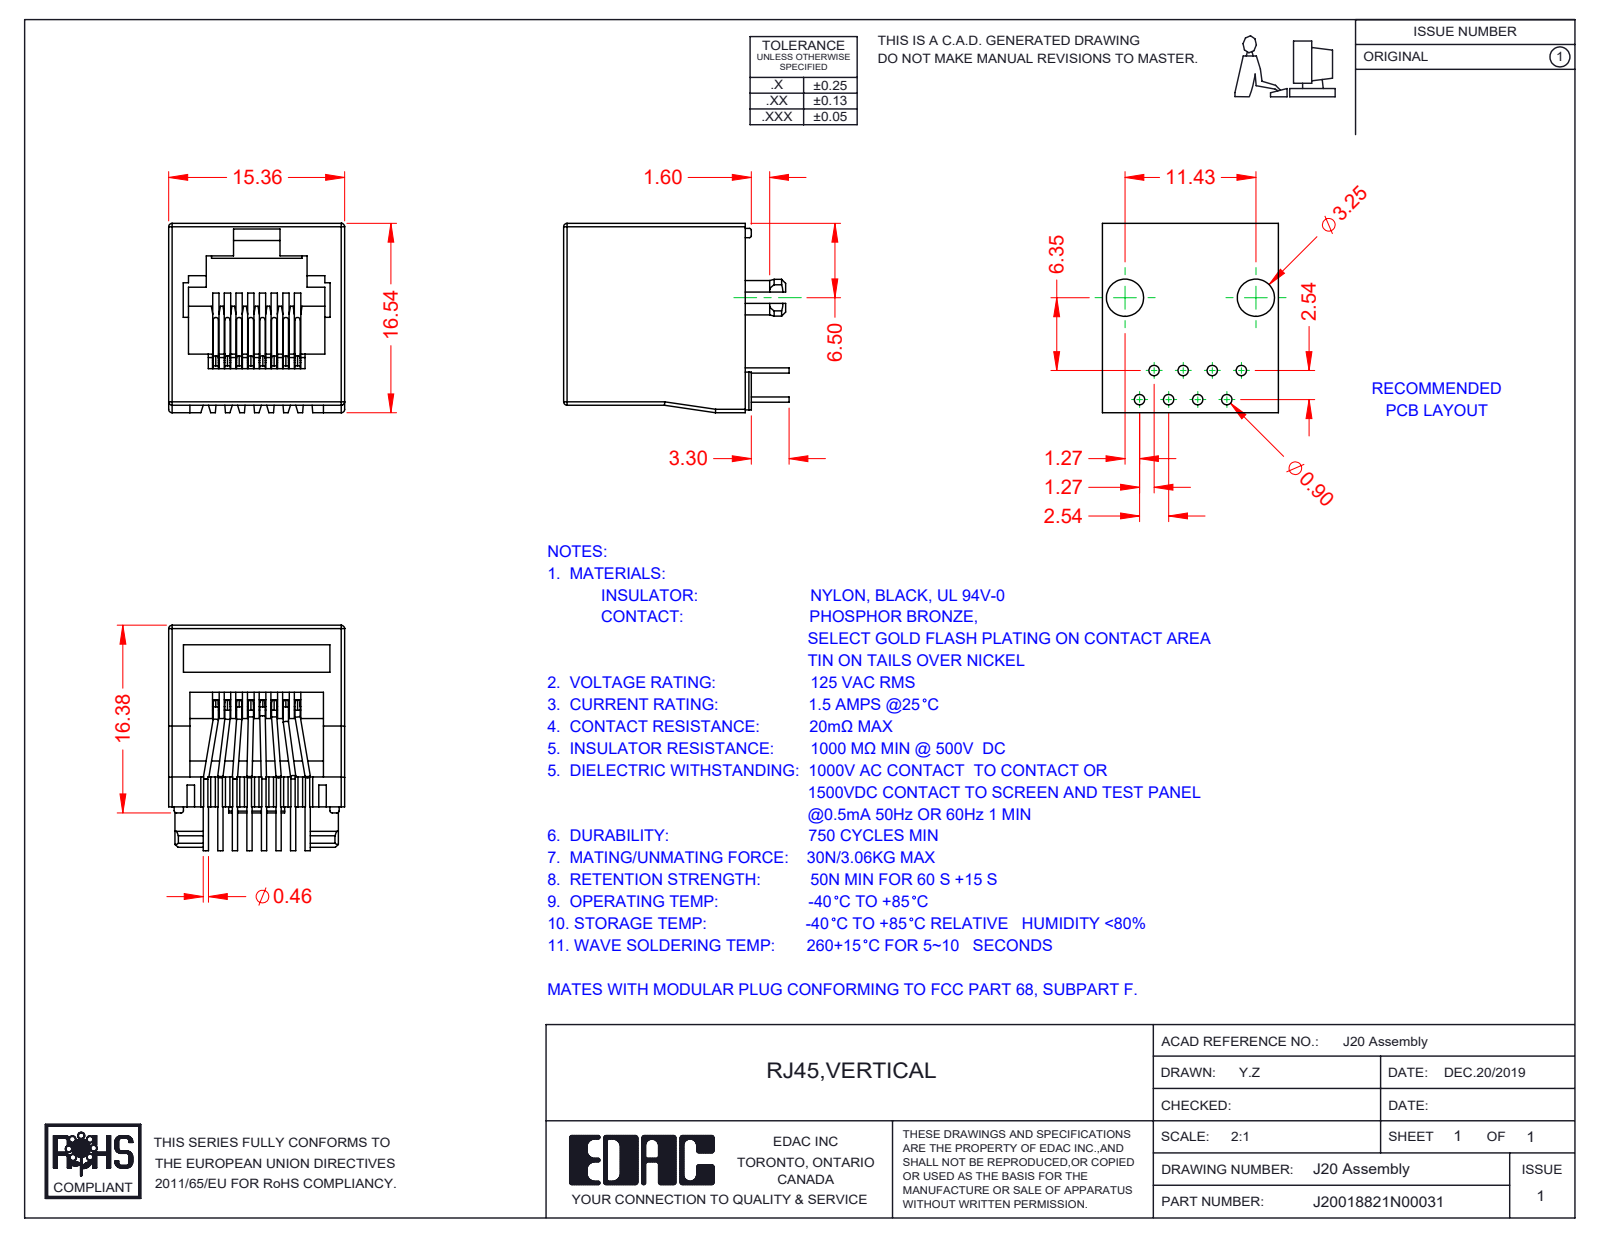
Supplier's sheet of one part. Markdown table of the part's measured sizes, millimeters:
| quantity | value |
| --- | --- |
| part name | 20 Contacts; 20 Insulator; RJ20018821N00031 |
| STEP written by | SolidWorks 2016 (CONFIG_CONTROL_DESIGN) |
| units | millimeters |
| bodies | 9 solids, 573 faces (332 planar, 193 cylindrical, 48 other) |
| overall size | 19.68 × 16.54 × 15.36 |
| volume | 1 935 mm³ |
| surface area | 3 110 mm² |
| round holes (diameter × count) | 2 × 2 |
| round bosses / shafts (diameter × count) | 0.46 × 45 |
| partial cylindrical surfaces (radius × count) | 0.13 × 16, 0.3 × 13, 0.25 × 9, 0.2 × 5, 0.15 × 2, 1.5 × 2, 1.6 × 2 |
| main face-to-face distances | 15.36, 1.73, 2, 13.63, 0.45, 15.85, 1.28, 10.35, 1.5, 14.08 |
| hole center spacings | 11.43 |
